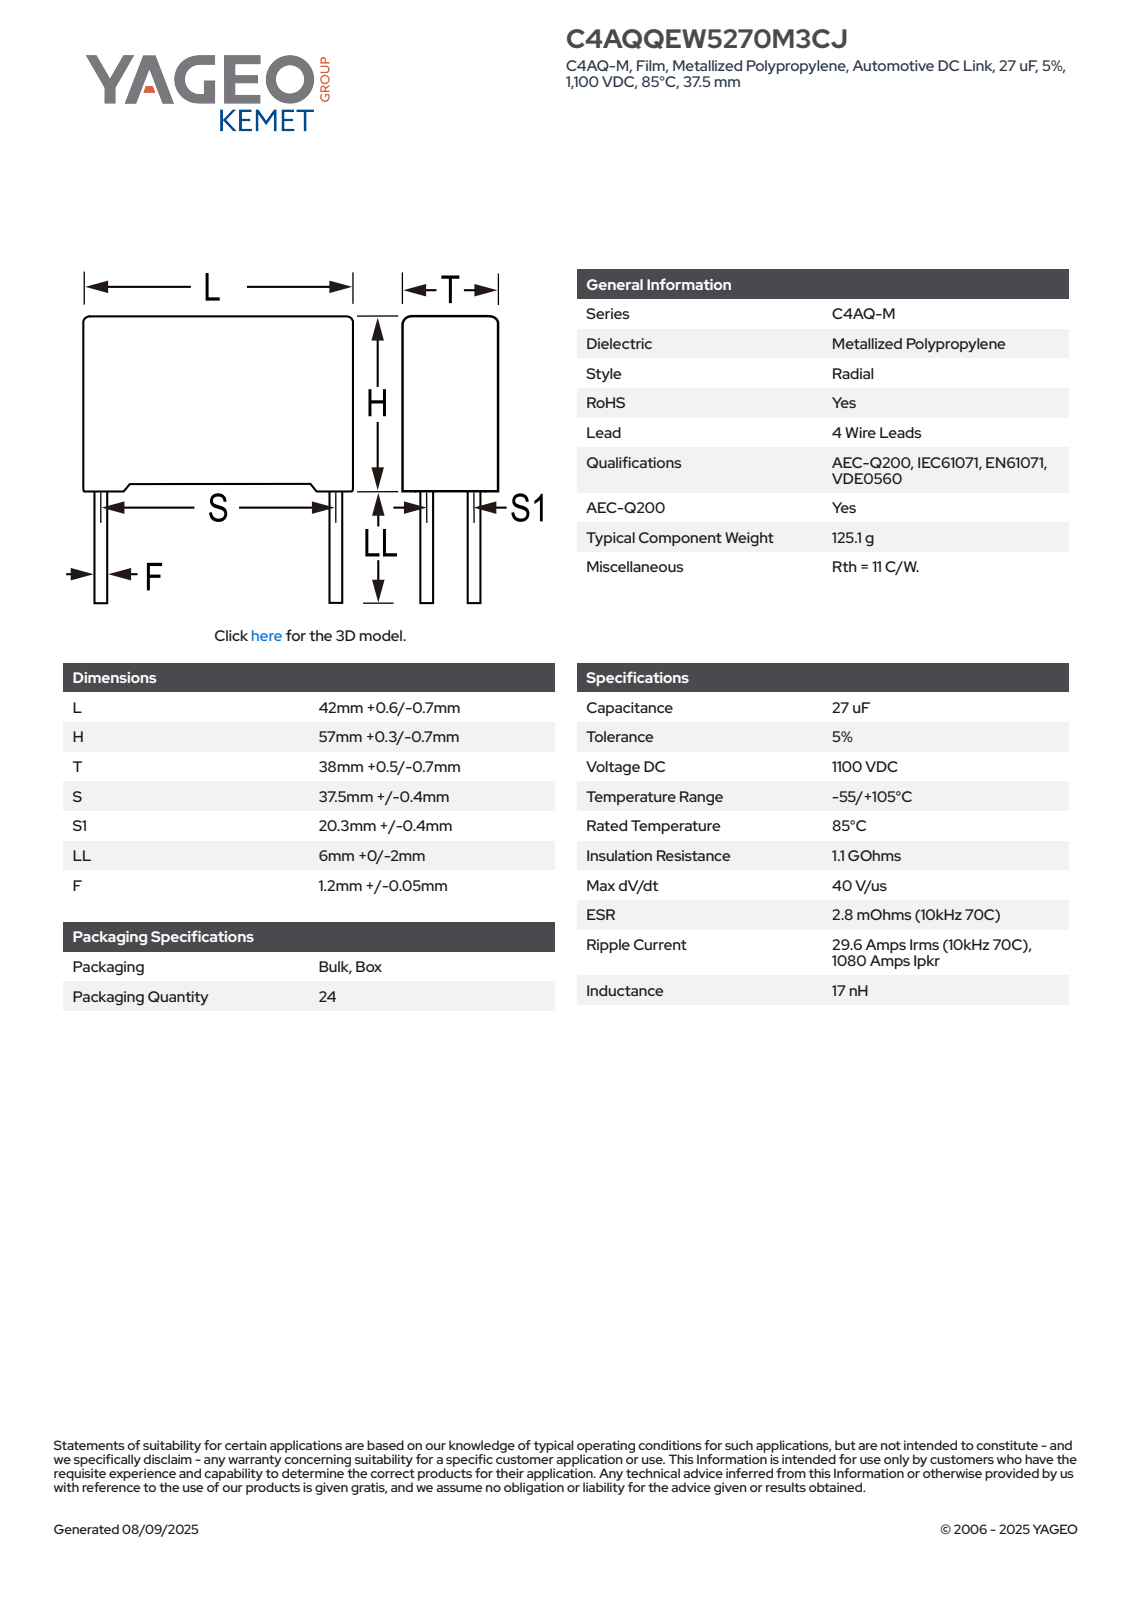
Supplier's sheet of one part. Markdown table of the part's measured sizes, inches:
| quantity | value |
| --- | --- |
| part name | CFP_RB4_42X57X38_L42.6H57.3T38.5S37.5S120.3LL6F1.25 |
| STEP written by | SolidWorks 2014 (AUTOMOTIVE_DESIGN) |
| units | inches |
| bodies | 4 solids, 91 faces (83 planar, 8 cylindrical, 0 other) |
| overall size | 2.492 × 1.677 × 1.516 |
| volume | 5.592 in³ |
| surface area | 19.93 in² |
| round bosses / shafts (diameter × count) | 0.049 × 4 |
| main face-to-face distances | 1.516, 1.677, 2.19, 0.066, 2.256, 0.093, 1.584, 1.491, 1.422, 1.329 |
